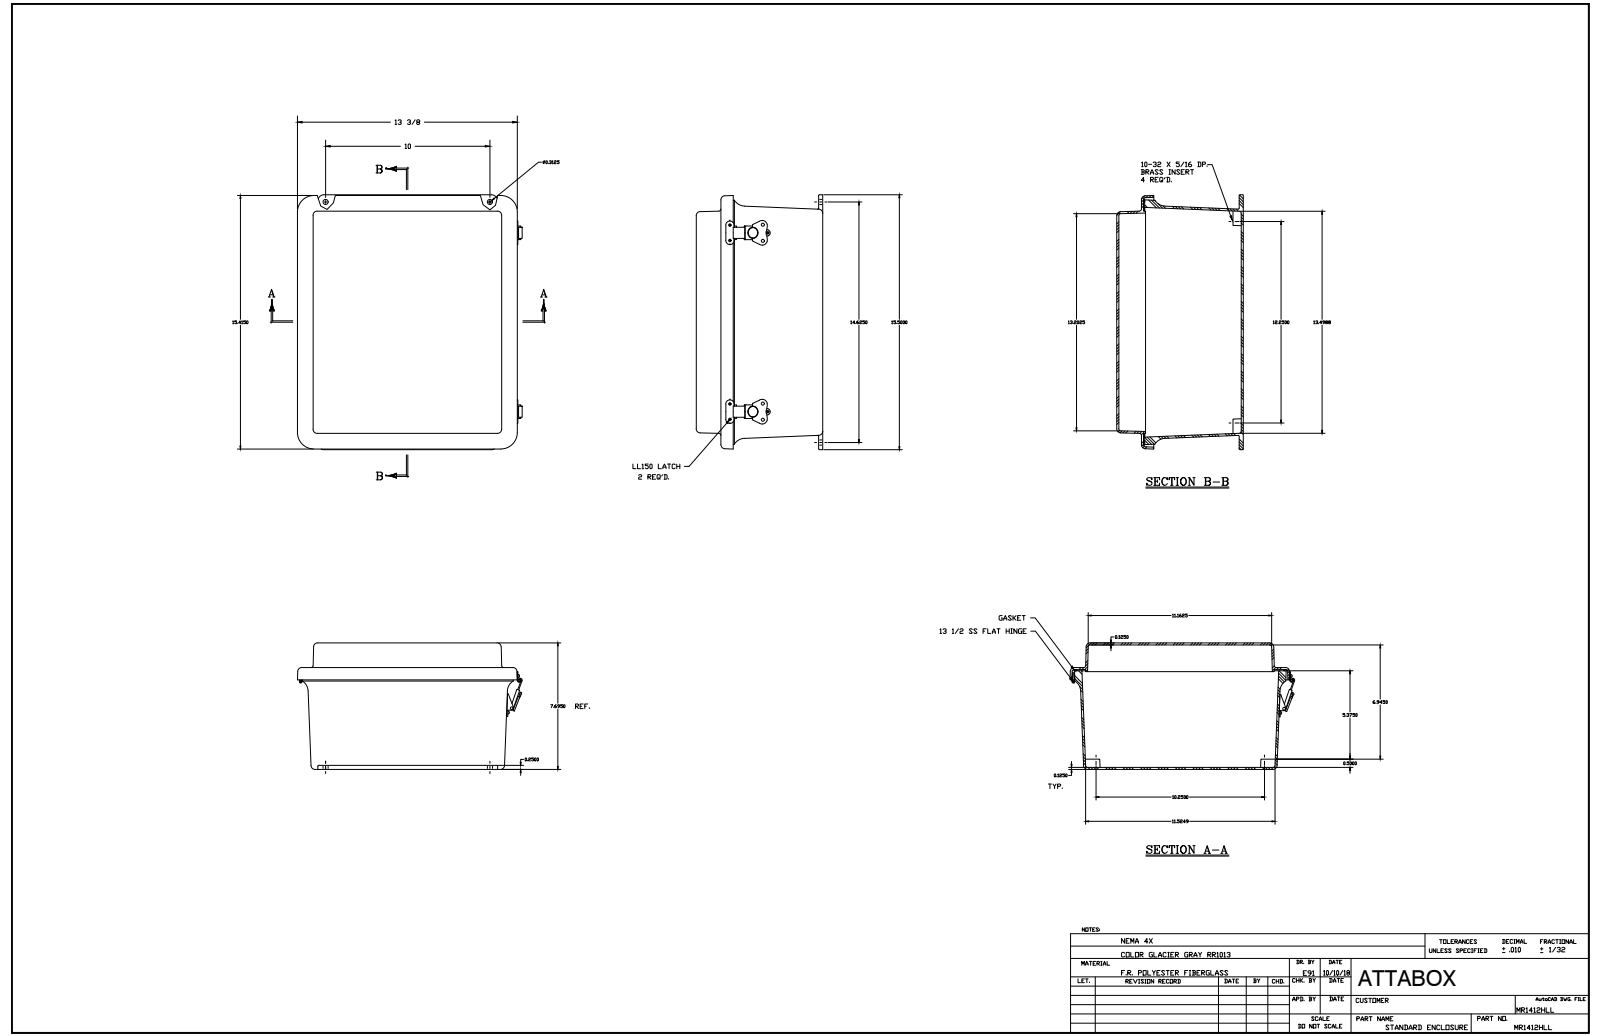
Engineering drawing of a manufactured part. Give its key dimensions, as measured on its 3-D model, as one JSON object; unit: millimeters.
{"part_name": "MR1412HLL", "step_written_by": "SolidWorks 2018 (AUTOMOTIVE_DESIGN)", "units": "millimeters", "bodies": {"solids": 50, "faces": 1275, "planar": 566, "cylindrical": 492, "other": 217}, "overall_size": [393.7, 344.9, 195.7], "volume_mm3": 1957000, "surface_area_mm2": 1123000, "round_holes": [[3.6, 18], [3.3, 10], [3.9, 8], [3.3, 4], [4, 4], [4.2, 4], [5, 4], [5.5, 4], [3, 2], [3.5, 2], [4.6, 2], [4.6, 2]], "round_bosses_or_shafts": [[6.4, 18], [3.2, 11], [3.2, 7], [6.9, 4], [14.8, 2], [13.3, 2], [5.3, 2], [4.7, 2]], "partial_cylinders_radius": [[0.8, 20], [3.2, 20], [6.4, 20], [2, 19], [0.9, 8], [1, 8], [1.1, 8], [1.2, 8]], "face_to_face_distances": [3.2, 3.2, 189.3, 192.5, 195.7, 192.5, 38.1, 151.2, 154.4, 41.3], "hole_center_spacings": [82.6, 165.1, 276.4, 247.7, 6.4, 76.2, 23.8, 34.8]}
